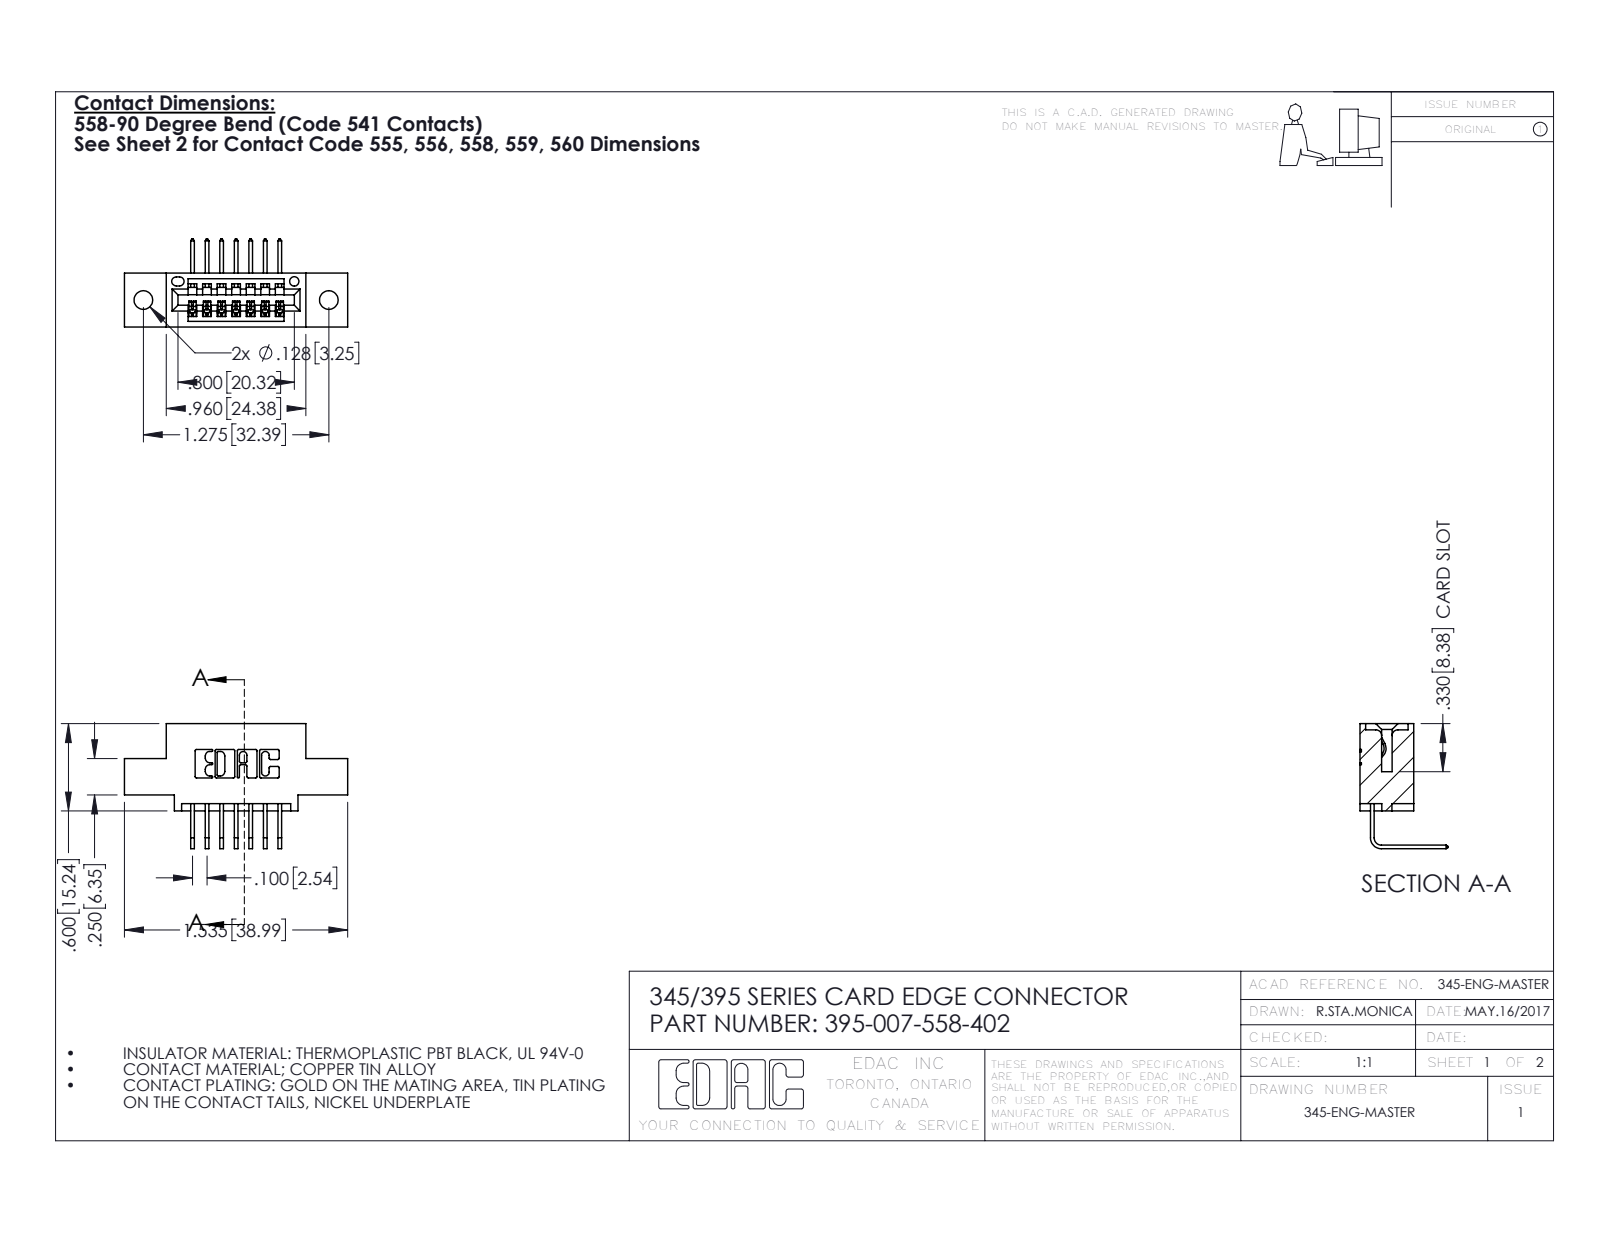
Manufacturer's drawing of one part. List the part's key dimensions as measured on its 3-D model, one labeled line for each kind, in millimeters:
Part name (STEP PRODUCT): 395-007-558-402; 345-292-001_558 Tail - 2; 345 Part_0.110 Offset - 0.128 Dia
STEP written by: SolidWorks 2016 (CONFIG_CONTROL_DESIGN)
Units: millimetres
Bodies: 8 solids, 550 faces (378 planar, 172 cylindrical, 0 other)
Overall size (bounding box): 39 × 21.8 × 15.4
Volume: 3 330 mm³ · Surface area: 3 897 mm²
Round holes (diameter × count): ⌀3.3 ×2, ⌀1.6 ×1
Partial cylindrical surfaces — rounded edges, fillets, slot ends (radius × count): R0.3 ×22, R0.2 ×14, R0.2 ×6, R0.8 ×6, R0.7 ×3, R0.8 ×2, R1 ×2, R0.4 ×1
Main face-to-face distances: 5.1, 9.4, 1.8, 7.6, 2.5, 7.6, 2.5, 6.9, 0.6, 4.1
Hole centre spacings: 6.9, 26.5, 32.4
